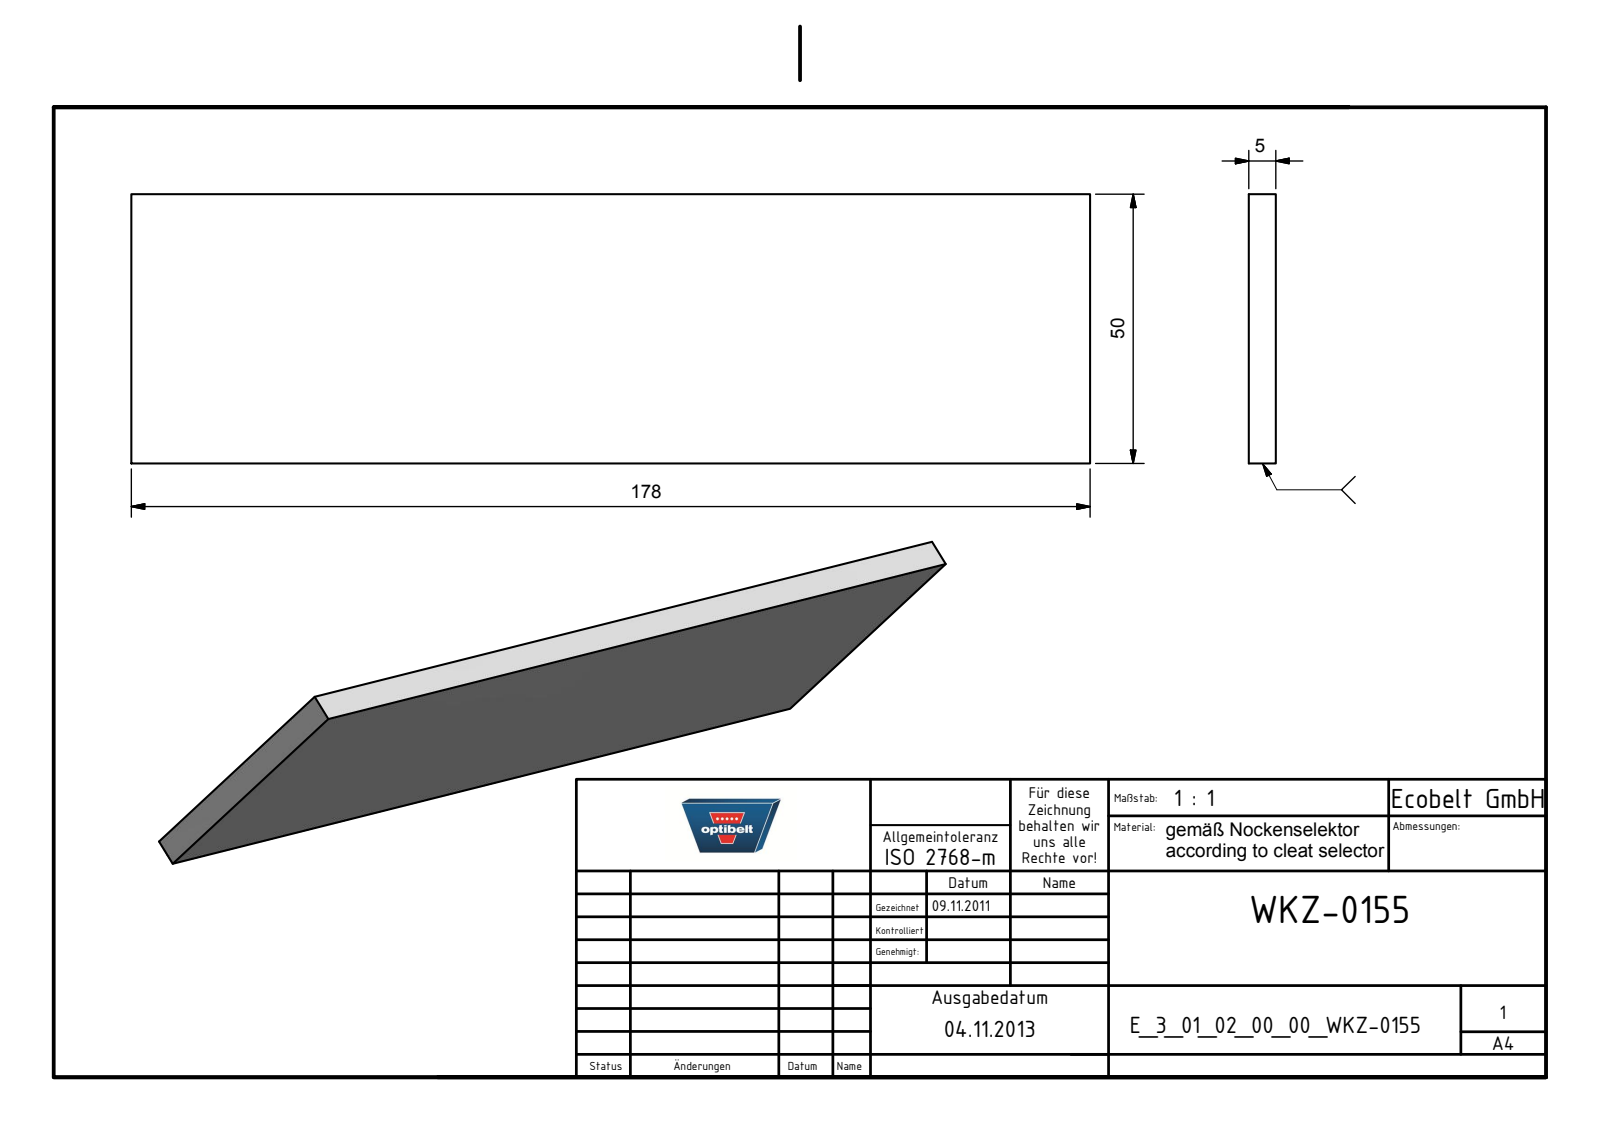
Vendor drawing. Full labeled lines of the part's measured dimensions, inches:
Part name (STEP PRODUCT): E_3_01_02_00_00_WKZ-0155
STEP written by: Autodesk Inventor 2021 (AUTOMOTIVE_DESIGN)
Units: inches
Bodies: 1 solid, 6 faces (6 planar, 0 cylindrical, 0 other)
Overall size (bounding box): 7.008 × 1.969 × 0.197
Volume: 2.716 in³ · Surface area: 31.12 in²
Main face-to-face distances: 0.197, 1.969, 7.008
